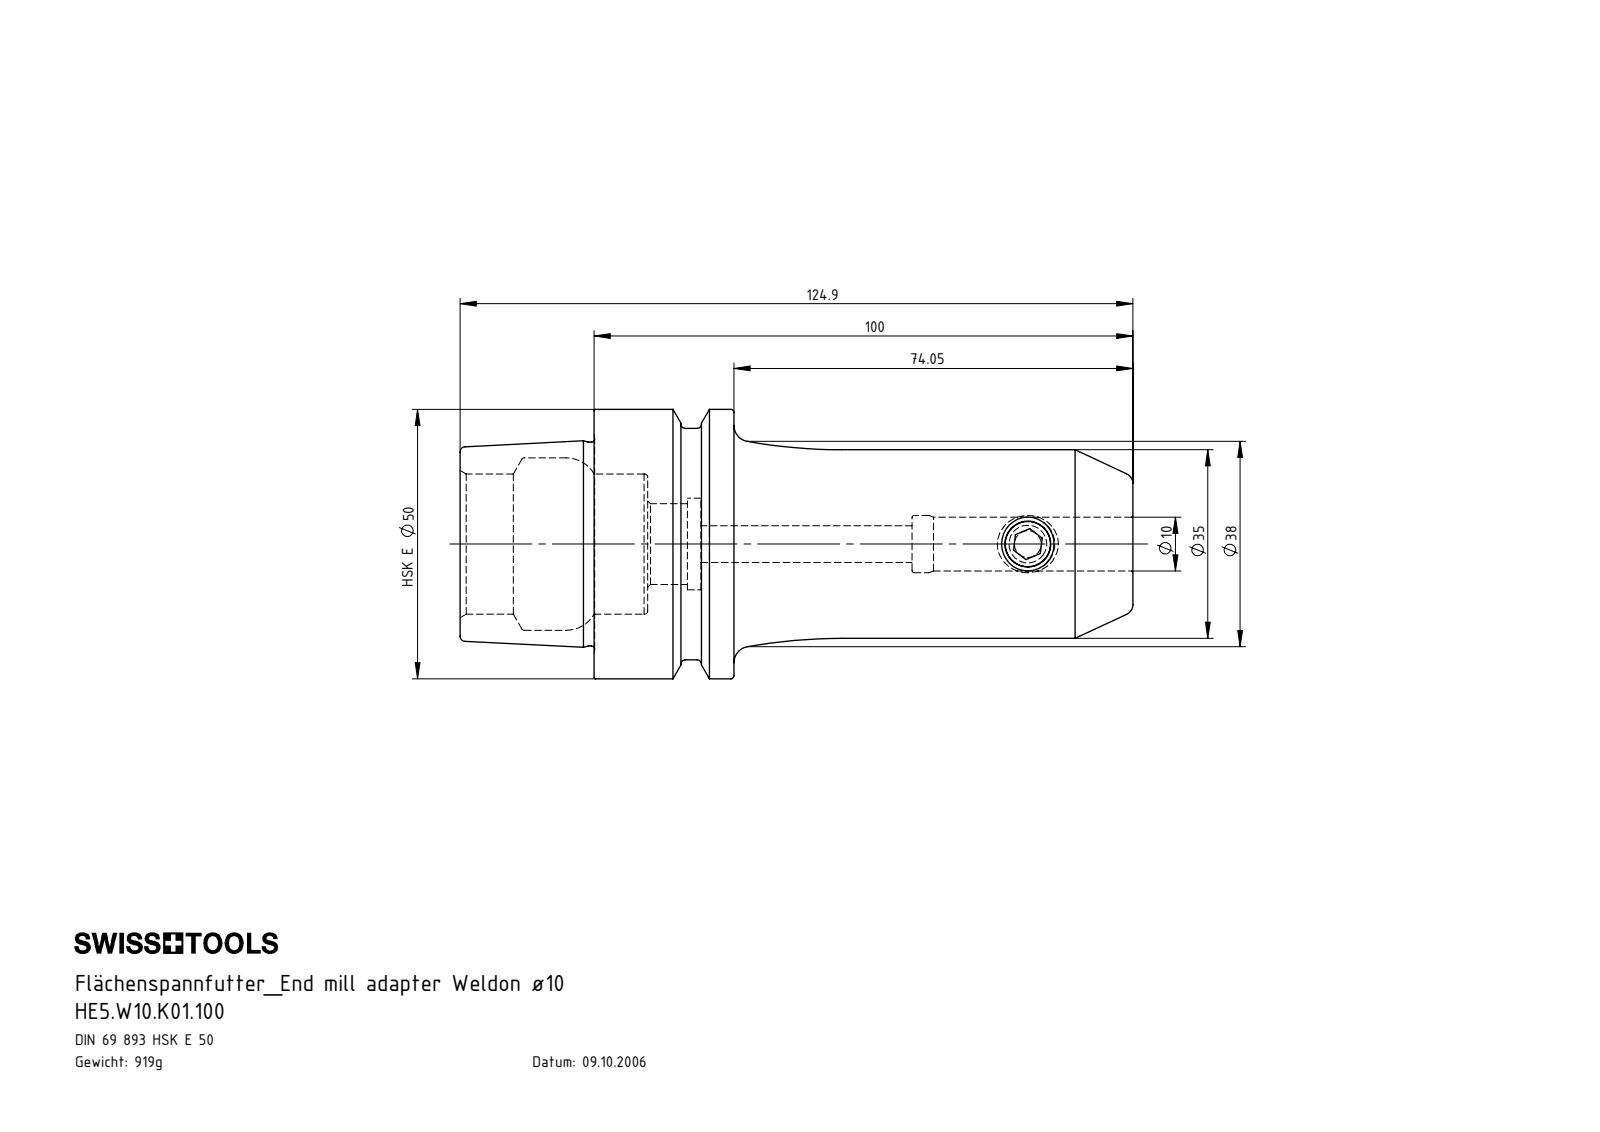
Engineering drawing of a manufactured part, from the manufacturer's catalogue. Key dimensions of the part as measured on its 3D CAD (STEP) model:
Part name (STEP PRODUCT): W10-ER1.001.012; HE5-W10.K01.100_B_Fertigbearbeitung; HE5.W10.K01.100
STEP written by: SolidWorks 2017 (AUTOMOTIVE_DESIGN)
Units: millimetres
Bodies: 2 solids, 111 faces (19 planar, 30 cylindrical, 62 other)
Overall size (bounding box): 124.9 × 50 × 50
Volume: 117 099 mm³ · Surface area: 25 331 mm²
Round holes (diameter × count): ⌀6.8 ×1, ⌀8.5 ×1, ⌀10 ×1, ⌀10.6 ×1, ⌀15 ×1, ⌀17 ×1, ⌀26 ×1, ⌀32 ×1
Round bosses / shafts (diameter × count): ⌀50 ×1, ⌀42.95 ×1, ⌀37.81 ×1, ⌀35 ×1, ⌀10 ×1
Main face-to-face distances: 25.95, 24.9, 50.85, 124.9, 100, 74.05, 34.85, 9.95, 16, 90.05
